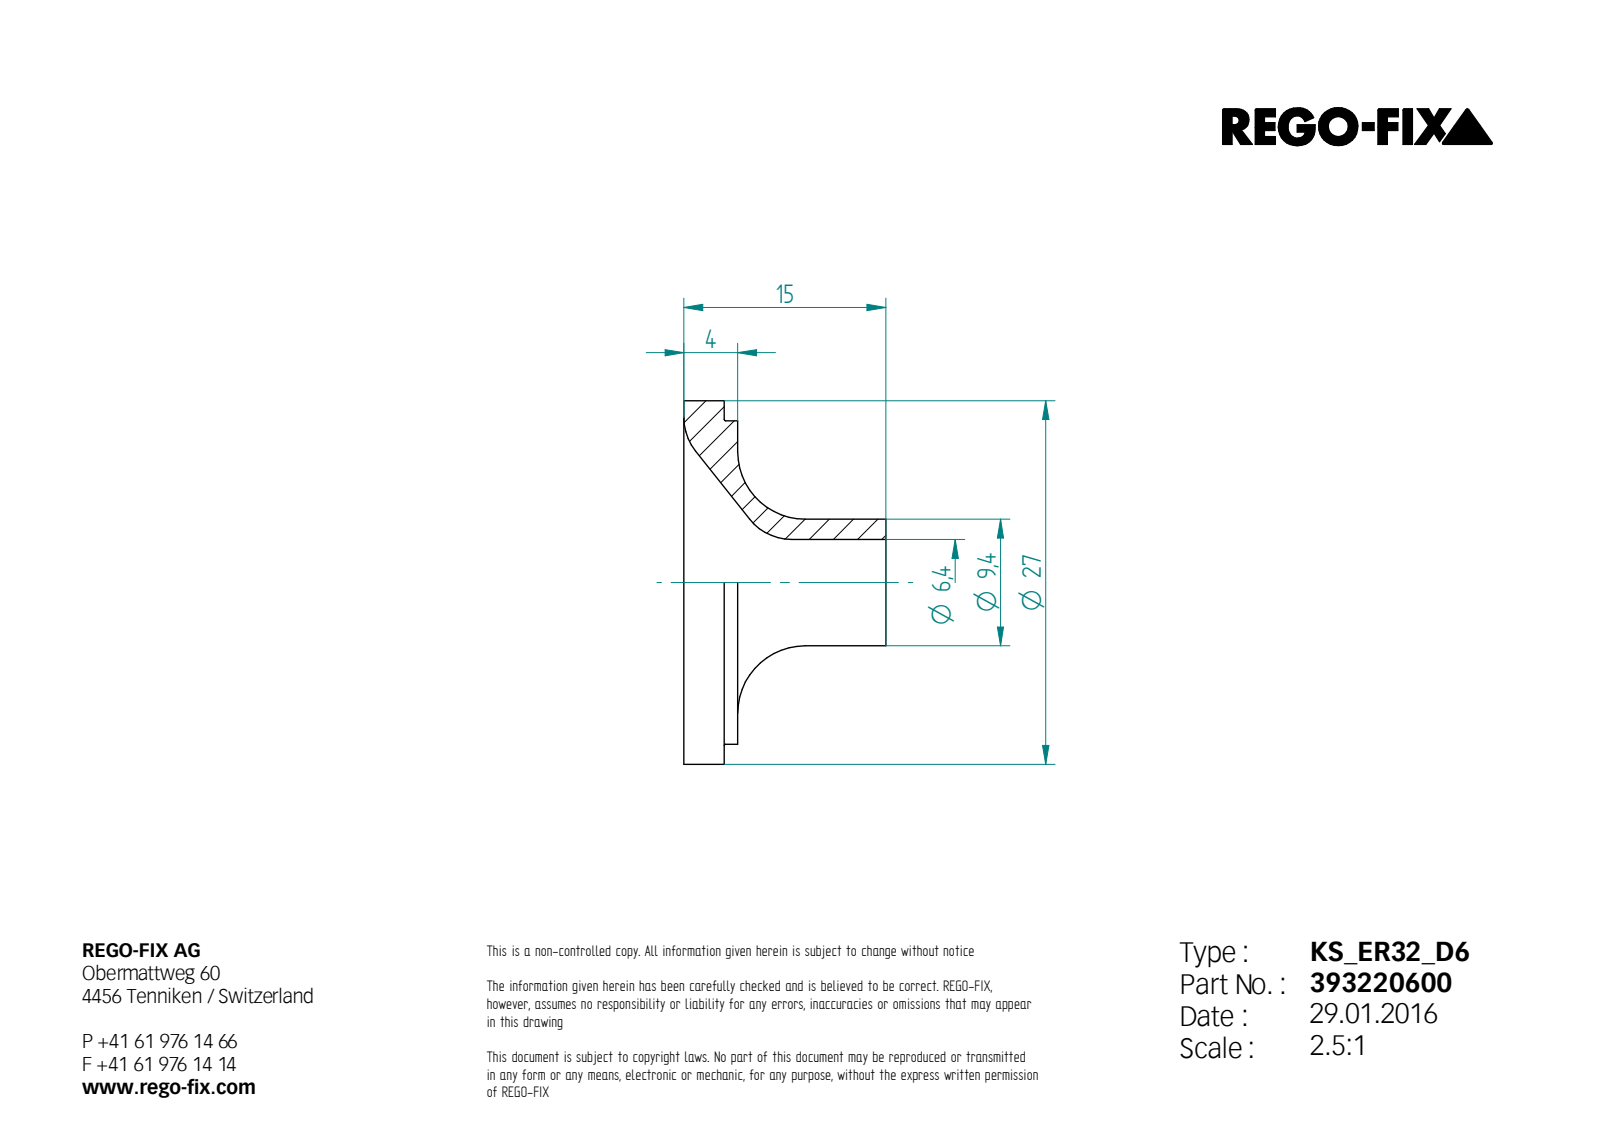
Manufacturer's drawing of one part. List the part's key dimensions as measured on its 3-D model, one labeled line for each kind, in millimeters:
STEP written by: Unknown (AUTOMOTIVE_DESIGN)
Units: millimetres
Bodies: 1 solid, 13 faces (4 planar, 4 cylindrical, 5 other)
Overall size (bounding box): 27 × 27 × 15
Volume: 1 782 mm³ · Surface area: 1 943 mm²
Round holes (diameter × count): ⌀6.4 ×1
Round bosses / shafts (diameter × count): ⌀27 ×1, ⌀24 ×1, ⌀9.4 ×1
Main face-to-face distances: 1, 3, 4, 15, 12, 11
